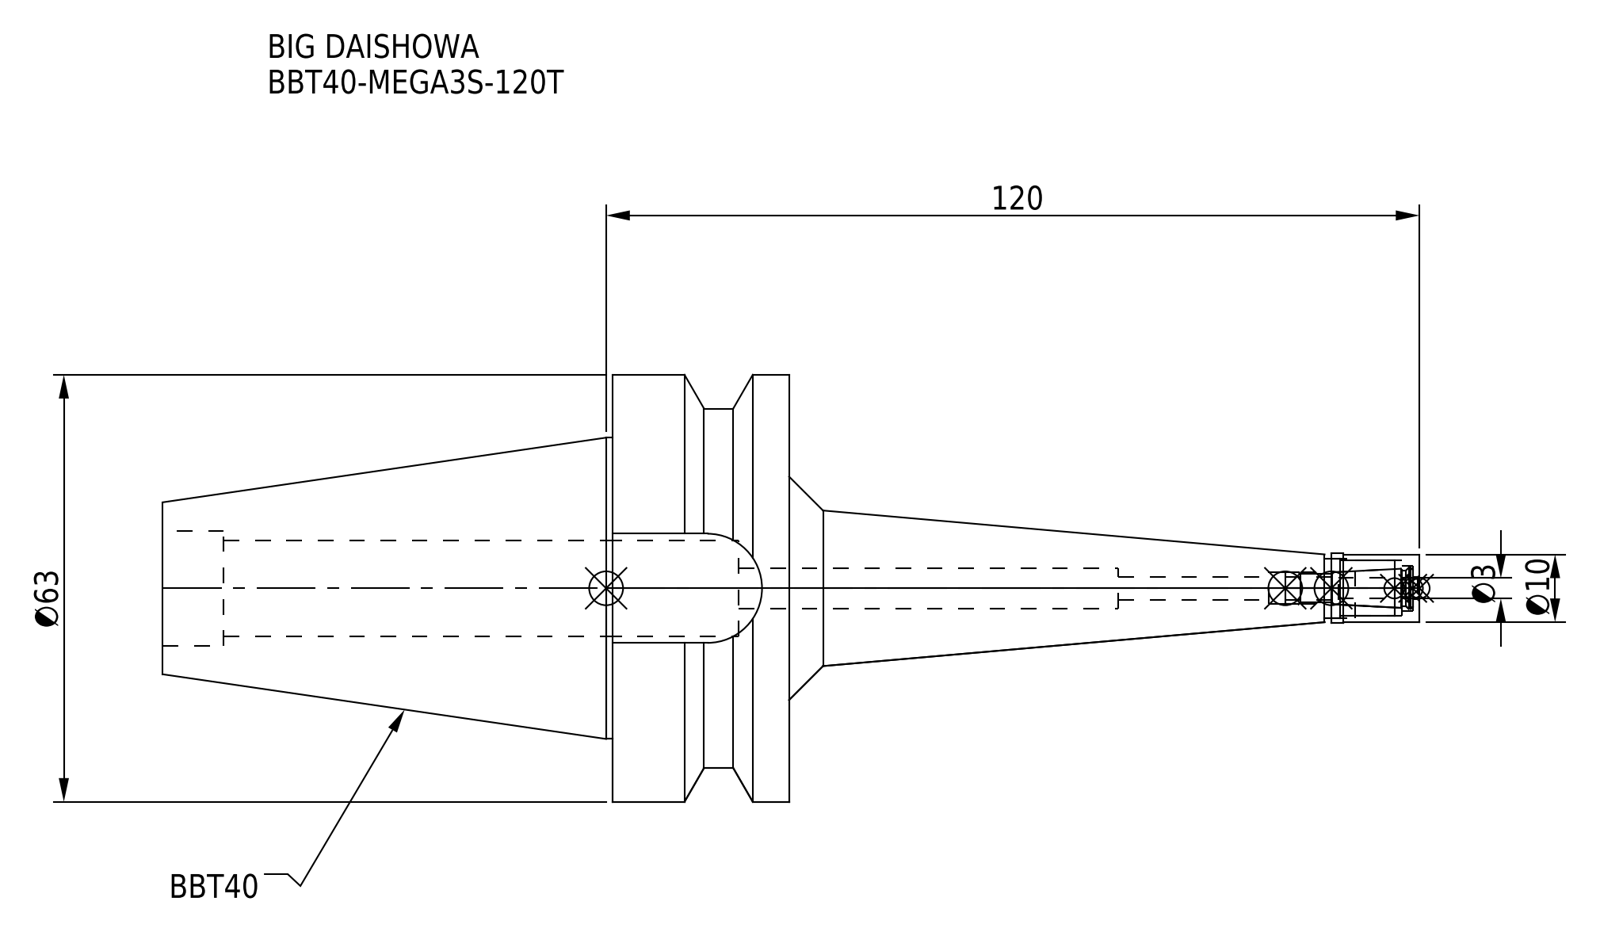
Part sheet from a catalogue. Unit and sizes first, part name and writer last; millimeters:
Units: millimetres
Overall size (bounding box): 185.4 × 63 × 63
Round holes (diameter × count): ⌀3.3 ×1, ⌀3.4 ×1, ⌀4.7 ×1, ⌀6 ×1, ⌀6.6 ×1, ⌀8.2 ×1, ⌀8.7 ×1, ⌀14.2 ×1, ⌀17 ×1
Round bosses / shafts (diameter × count): ⌀63 ×1, ⌀53 ×1, ⌀44.45 ×1, ⌀10.3 ×1, ⌀10 ×1
Partial cylindrical surfaces — rounded edges, fillets, slot ends (radius × count): R8.05 ×1
Main face-to-face distances: 26, 45, 92.4, 66.4, 16.1, 7.4, 18.6, 85, 83.4, 76
Volume: 139 998 mm³ · Surface area: 29 073 mm²
Bodies: 2 solids, 74 faces (22 planar, 38 cylindrical, 14 other)
Part name (STEP PRODUCT): DXF_TEMP_ASSY_ASM_4_ASM.stp; BBT40-MEGA3S-120T-030-FreeParts; BBT40-MEGA3S-120T; BBT40MS03120T-030_ASM.stp (+3 more)
STEP written by: SolidWorks 2019 (CONFIG_CONTROL_DESIGN)
